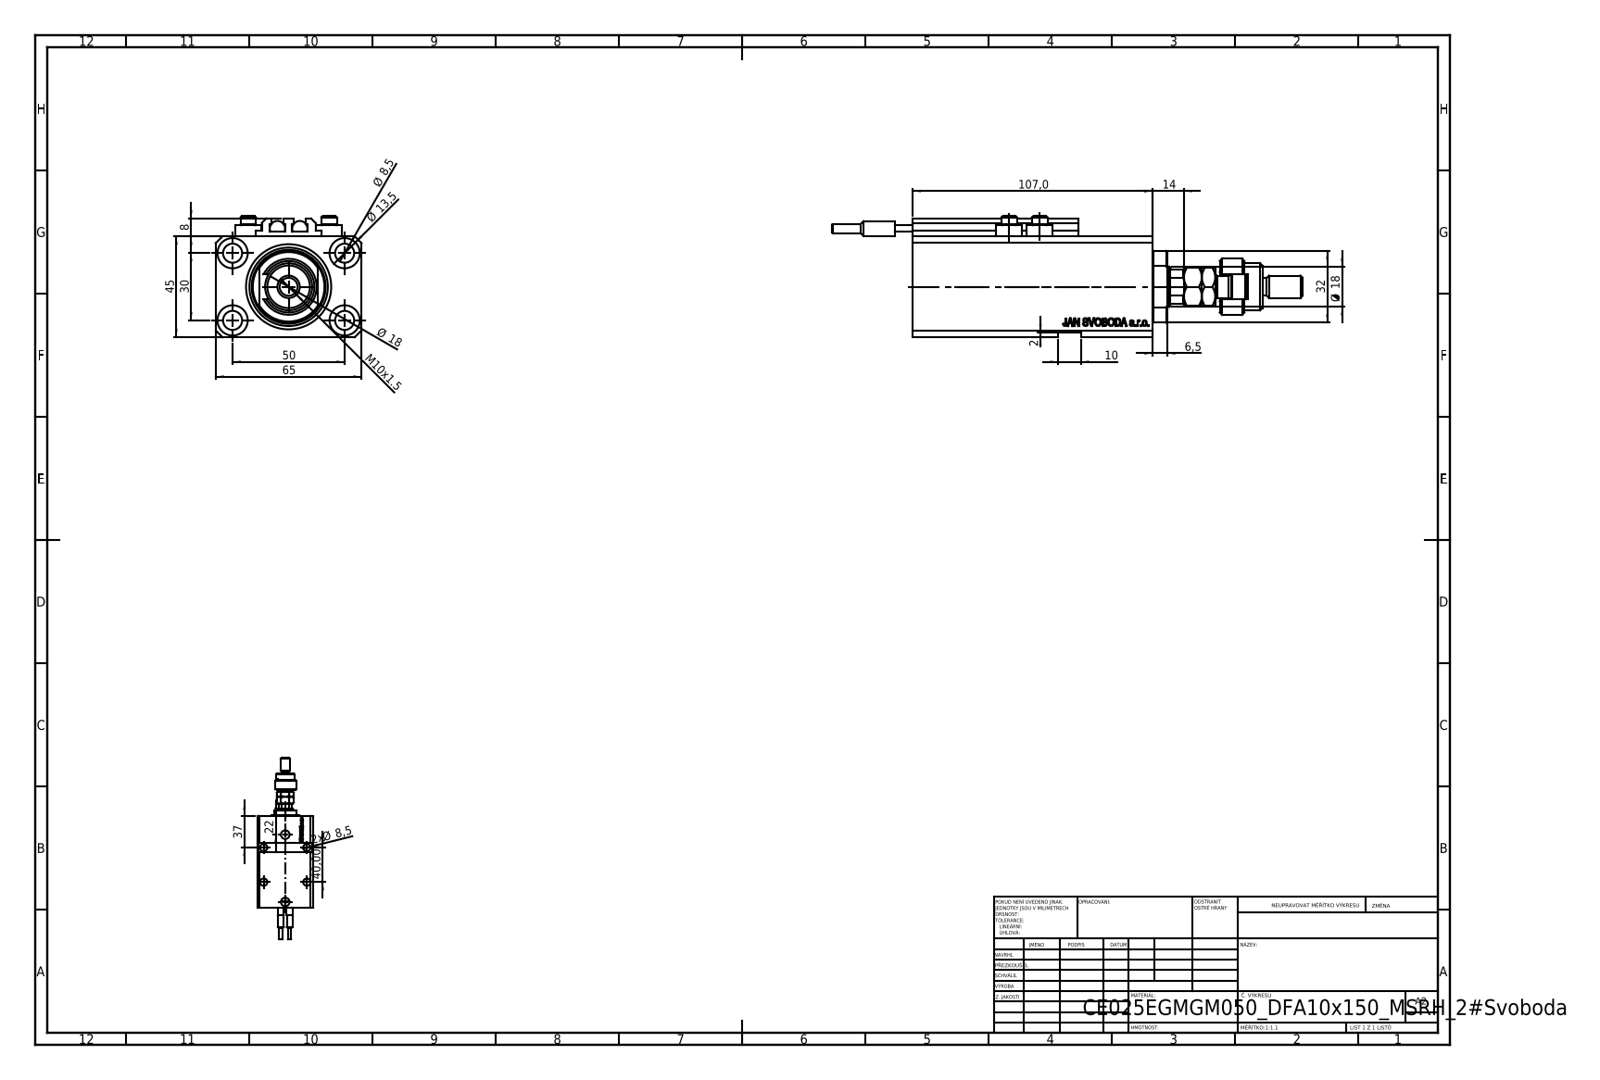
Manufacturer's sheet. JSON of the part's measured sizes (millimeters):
{"part_name": "FEMALE_PART_FOR_DFA; MFA; V250CE_VC_E; ALLEN BOLT V250CE (+3 more)", "step_written_by": "SolidWorks 2019 (CONFIG_CONTROL_DESIGN)", "units": "millimeters", "bodies": {"solids": 12, "faces": 1224, "planar": 571, "cylindrical": 171, "other": 482}, "overall_size": [210, 65, 54], "volume_mm3": 288767, "surface_area_mm2": 85071, "round_holes": [[8.5, 9], [1.25, 4], [4, 4], [13.5, 4], [10, 2], [13.16, 2], [20, 2], [18, 1], [38, 1]], "round_bosses_or_shafts": [[11.6, 4], [7, 4], [6.8, 2], [6.5, 2], [4, 2], [25, 1], [21, 1], [16, 1]], "partial_cylinders_radius": [[0.2, 10], [5.5, 1], [8.5, 1], [8.75, 1], [16, 1]], "face_to_face_distances": [45, 65, 14, 2, 47, 3, 93, 107, 5, 10], "hole_center_spacings": [29.15, 50, 13.6, 14.76, 15.12, 27.51, 27.89, 30]}
